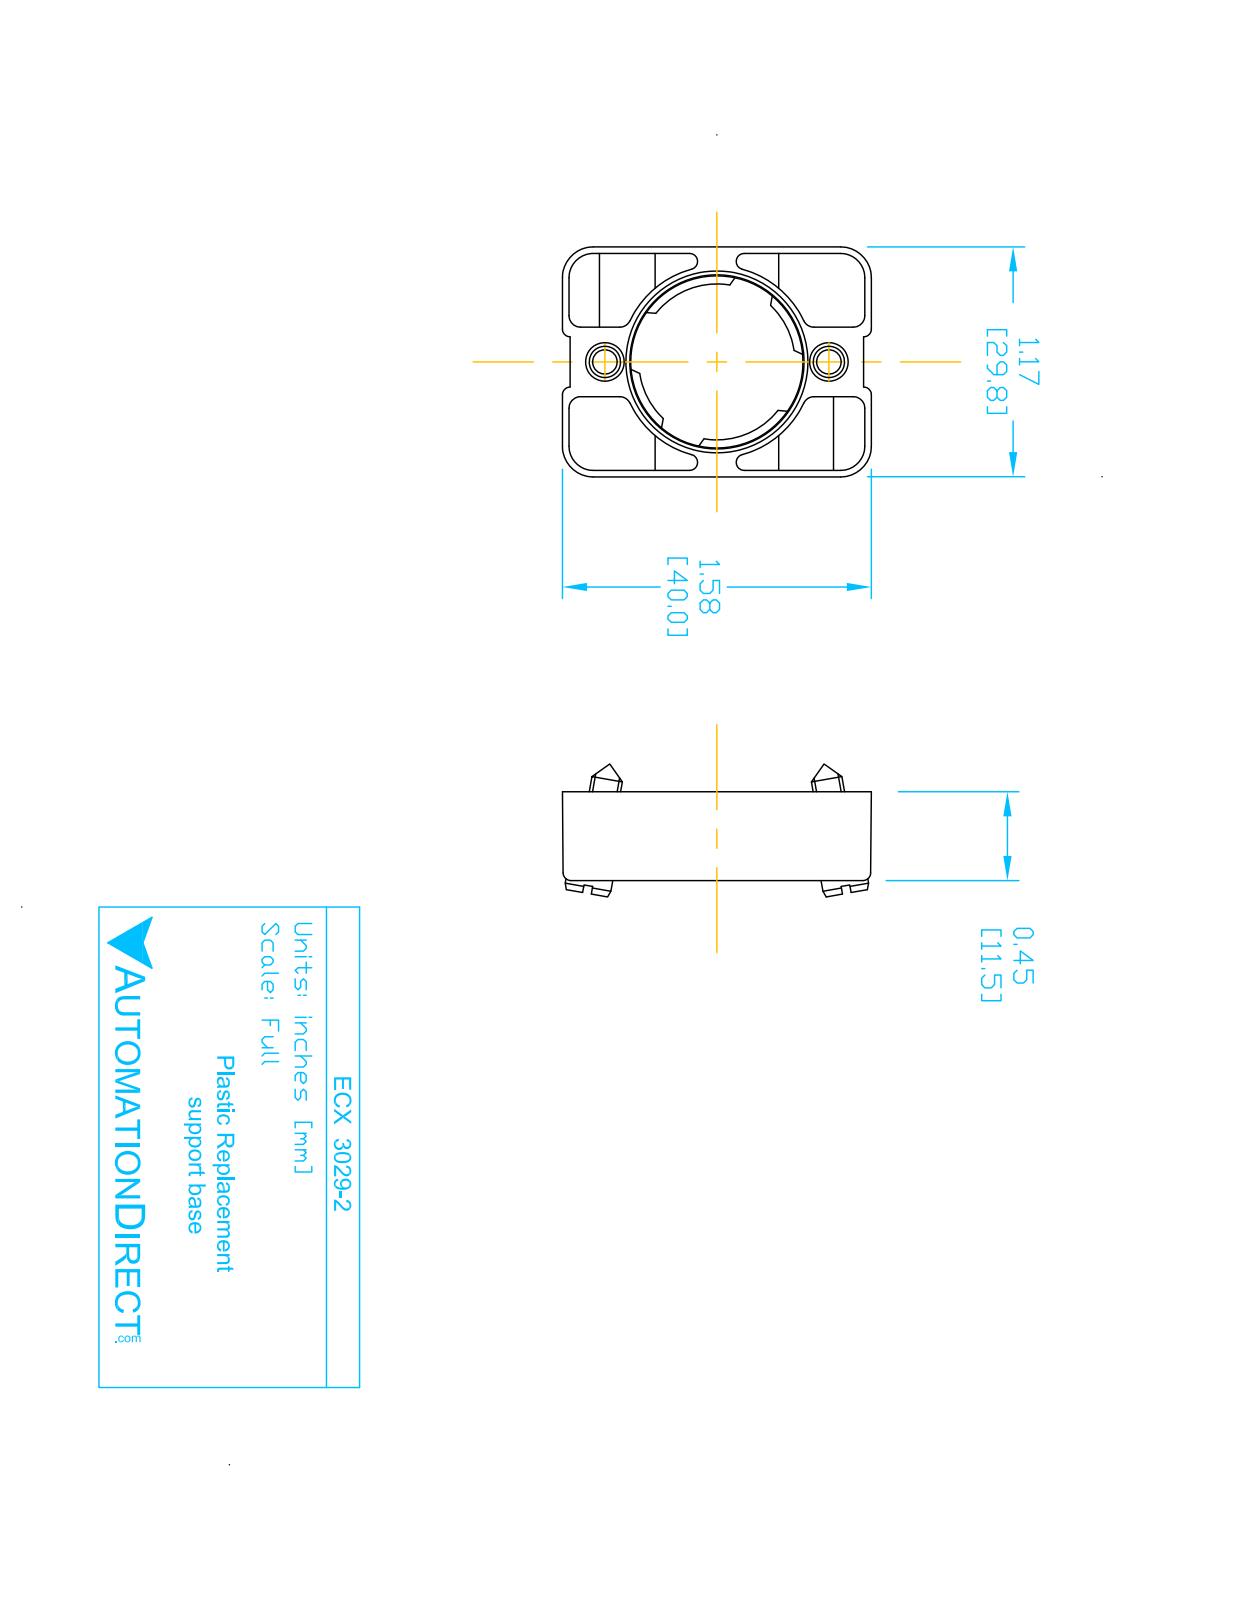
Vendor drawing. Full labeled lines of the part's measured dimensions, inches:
Part name (STEP PRODUCT): ECX3029-2
STEP written by: SolidWorks 2017 (AUTOMOTIVE_DESIGN)
Units: inches
Bodies: 3 solids, 235 faces (122 planar, 97 cylindrical, 16 other)
Overall size (bounding box): 1.581 × 1.178 × 0.834
Volume: 0.253 in³ · Surface area: 10.28 in²
Round holes (diameter × count): ⌀0.124 ×2, ⌀0.13 ×2, ⌀0.197 ×1, ⌀0.878 ×1, ⌀0.888 ×1
Round bosses / shafts (diameter × count): ⌀0.157 ×2
Partial cylindrical surfaces — rounded edges, fillets, slot ends (radius × count): R0.059 ×24, R0.041 ×12, R0.124 ×12, R0.157 ×12, R0.039 ×4, R0.128 ×2, R0.398 ×1, R0.49 ×1
Main face-to-face distances: 0.033, 0.031, 1.143, 1.142, 1.144, 0.435, 0.404, 1.141, 1.541, 1.175
